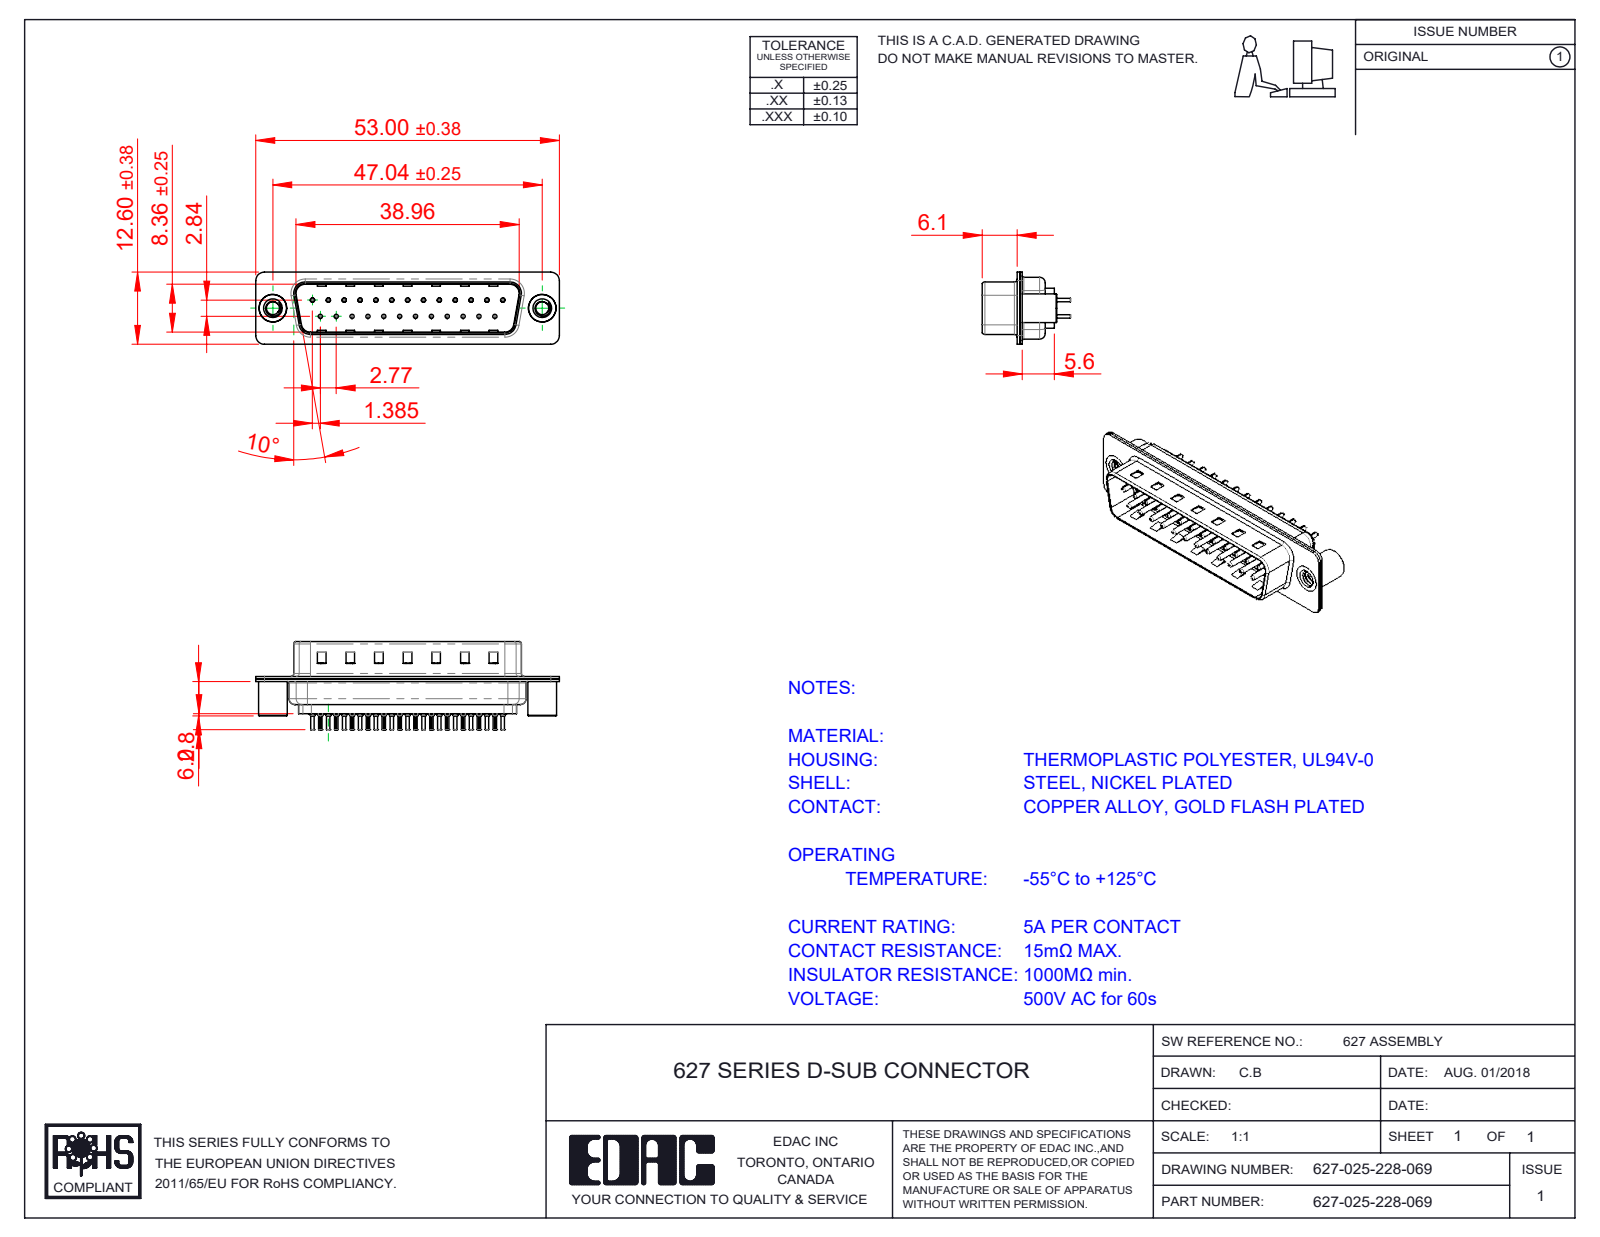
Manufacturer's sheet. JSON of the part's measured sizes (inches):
{"part_name": "627 Housing_25 FF; 627 Contact Row 1_28L; 627 Contact Row 2_28L; 627 4-40 Threaded Standoff BS (+3 more)", "step_written_by": "SolidWorks 2020 (CONFIG_CONTROL_DESIGN)", "units": "inches", "bodies": {"solids": 31, "faces": 2909, "planar": 777, "cylindrical": 1137, "other": 995}, "overall_size": [2.087, 0.74, 0.496], "volume_in3": 0.206, "surface_area_in2": 14.13, "round_holes": [[0.008, 25], [0.014, 25], [0.043, 25], [0.063, 25], [0.089, 2], [0.157, 2], [0.189, 2]], "round_bosses_or_shafts": [[0.079, 25], [0.059, 25], [0.03, 25], [0.024, 25], [0.197, 2], [0.193, 2]], "partial_cylinders_radius": [[0.004, 50], [0.059, 16], [0.079, 12], [0.02, 8], [0.063, 8], [0.01, 4], [0.024, 4], [0.026, 4]], "face_to_face_distances": [0.016, 0.018, 0.238, 0.032, 0.377, 0.331, 0.059, 0.027, 0.302, 0.035], "hole_center_spacings": [0.124, 0.109, 0.218, 0.327, 0.436, 0.545, 0.198, 0.295]}
